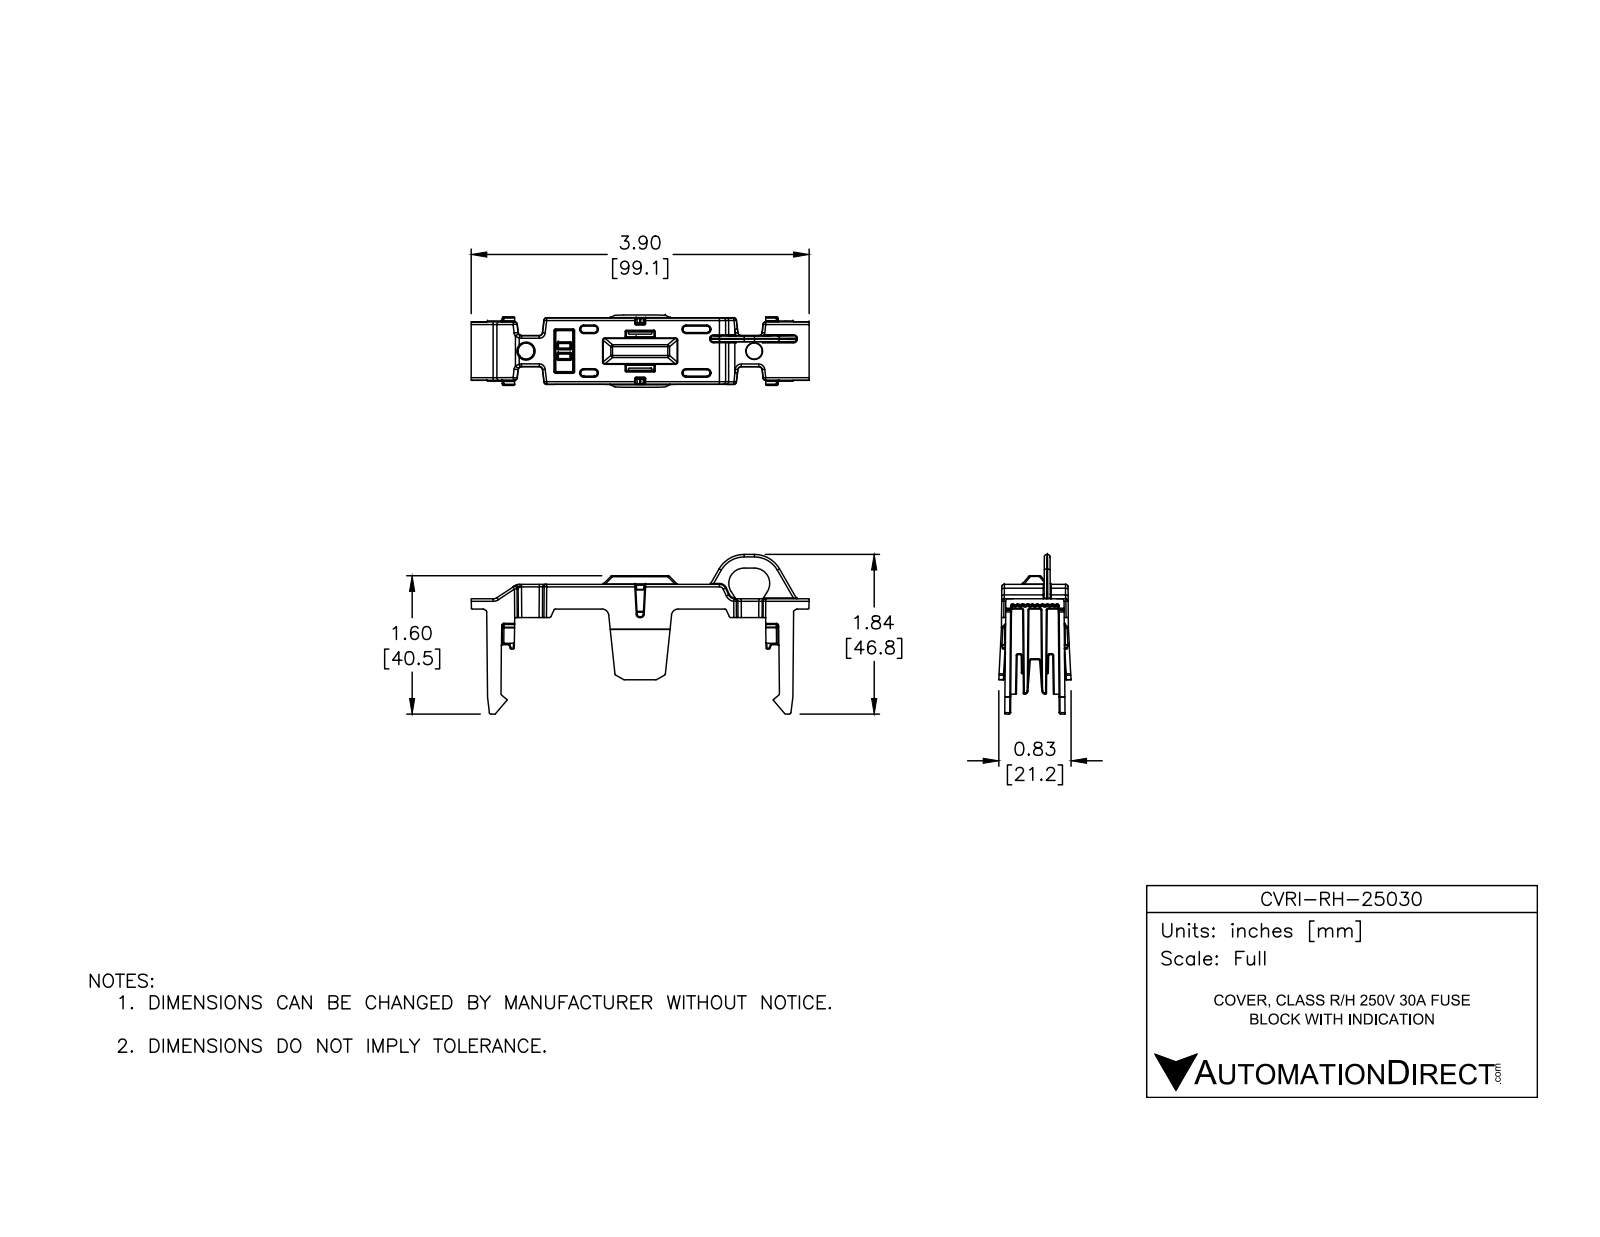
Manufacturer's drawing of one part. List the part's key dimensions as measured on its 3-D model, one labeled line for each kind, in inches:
Part name (STEP PRODUCT): CVRI-RH-25030
STEP written by: SolidWorks 2016 (AUTOMOTIVE_DESIGN)
Units: inches
Bodies: 1 solid, 2459 faces (431 planar, 1074 cylindrical, 954 other)
Overall size (bounding box): 3.901 × 1.842 × 0.834
Volume: 0.558 in³ · Surface area: 19.27 in²
Partial cylindrical surfaces — rounded edges, fillets, slot ends (radius × count): R0.01 ×320, R0.006 ×277, R0.03 ×48, R0.039 ×39, R0.008 ×38, R0.02 ×18, R0.018 ×9, R0.016 ×8
Main face-to-face distances: 0.059, 0.059, 0.047, 0.098, 0.012, 0.108, 0.157, 3.271, 0.167, 0.114
